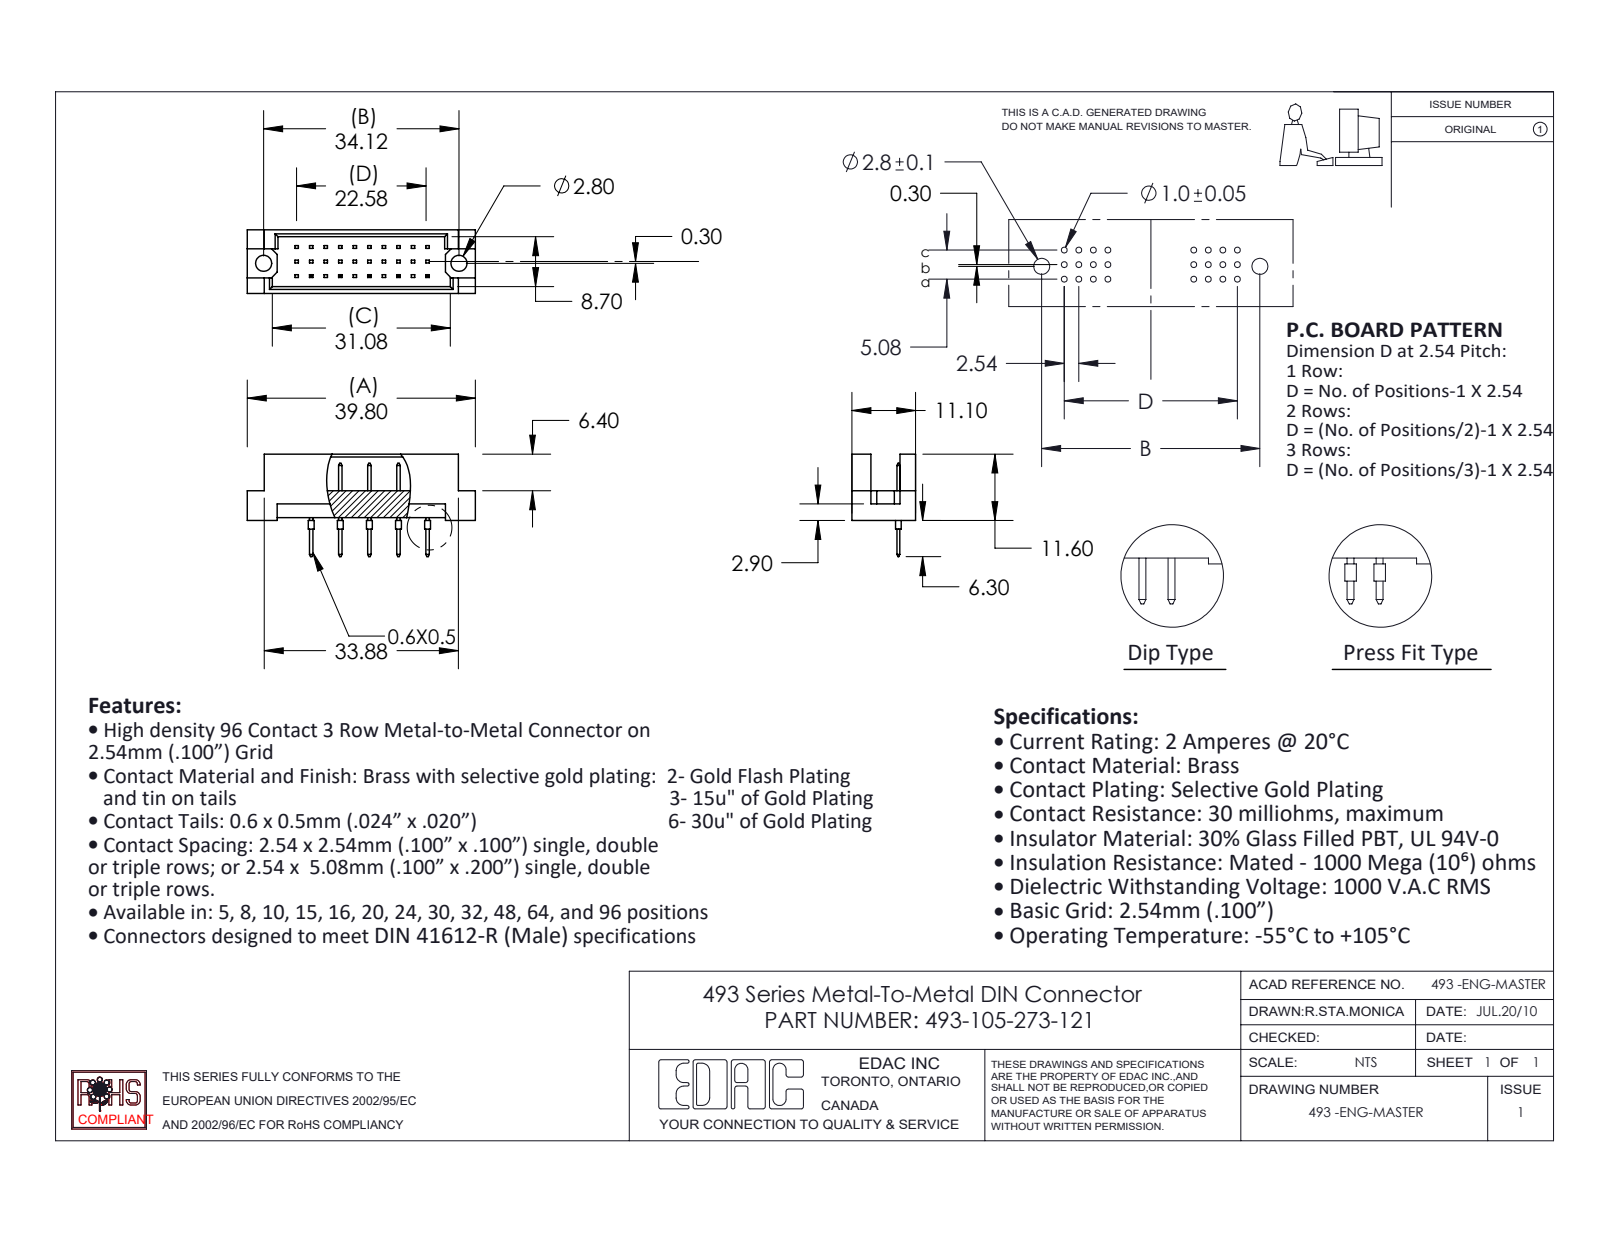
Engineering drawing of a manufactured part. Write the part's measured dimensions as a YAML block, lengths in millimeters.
part_name: "493-105-273-122; 493-290_73; 493 Part_30"
step_written_by: "SolidWorks 2020 (CONFIG_CONTROL_DESIGN)"
units: millimeters
bodies: {solids: 6, faces: 282, planar: 268, cylindrical: 14, other: 0}
overall_size: [39.8, 17.9, 11.1]
volume: 2401
surface_area: 2927
round_holes:
  - {diameter: 2.8, count: 2}
round_bosses_or_shafts:
  - {diameter: 1, count: 5}
face_to_face_distances: [1.2, 9.9, 11.1, 8.7, 4.7, 0.5, 5.08, 2.4, 2.54, 2.3]
hole_center_spacings: [34.12]
